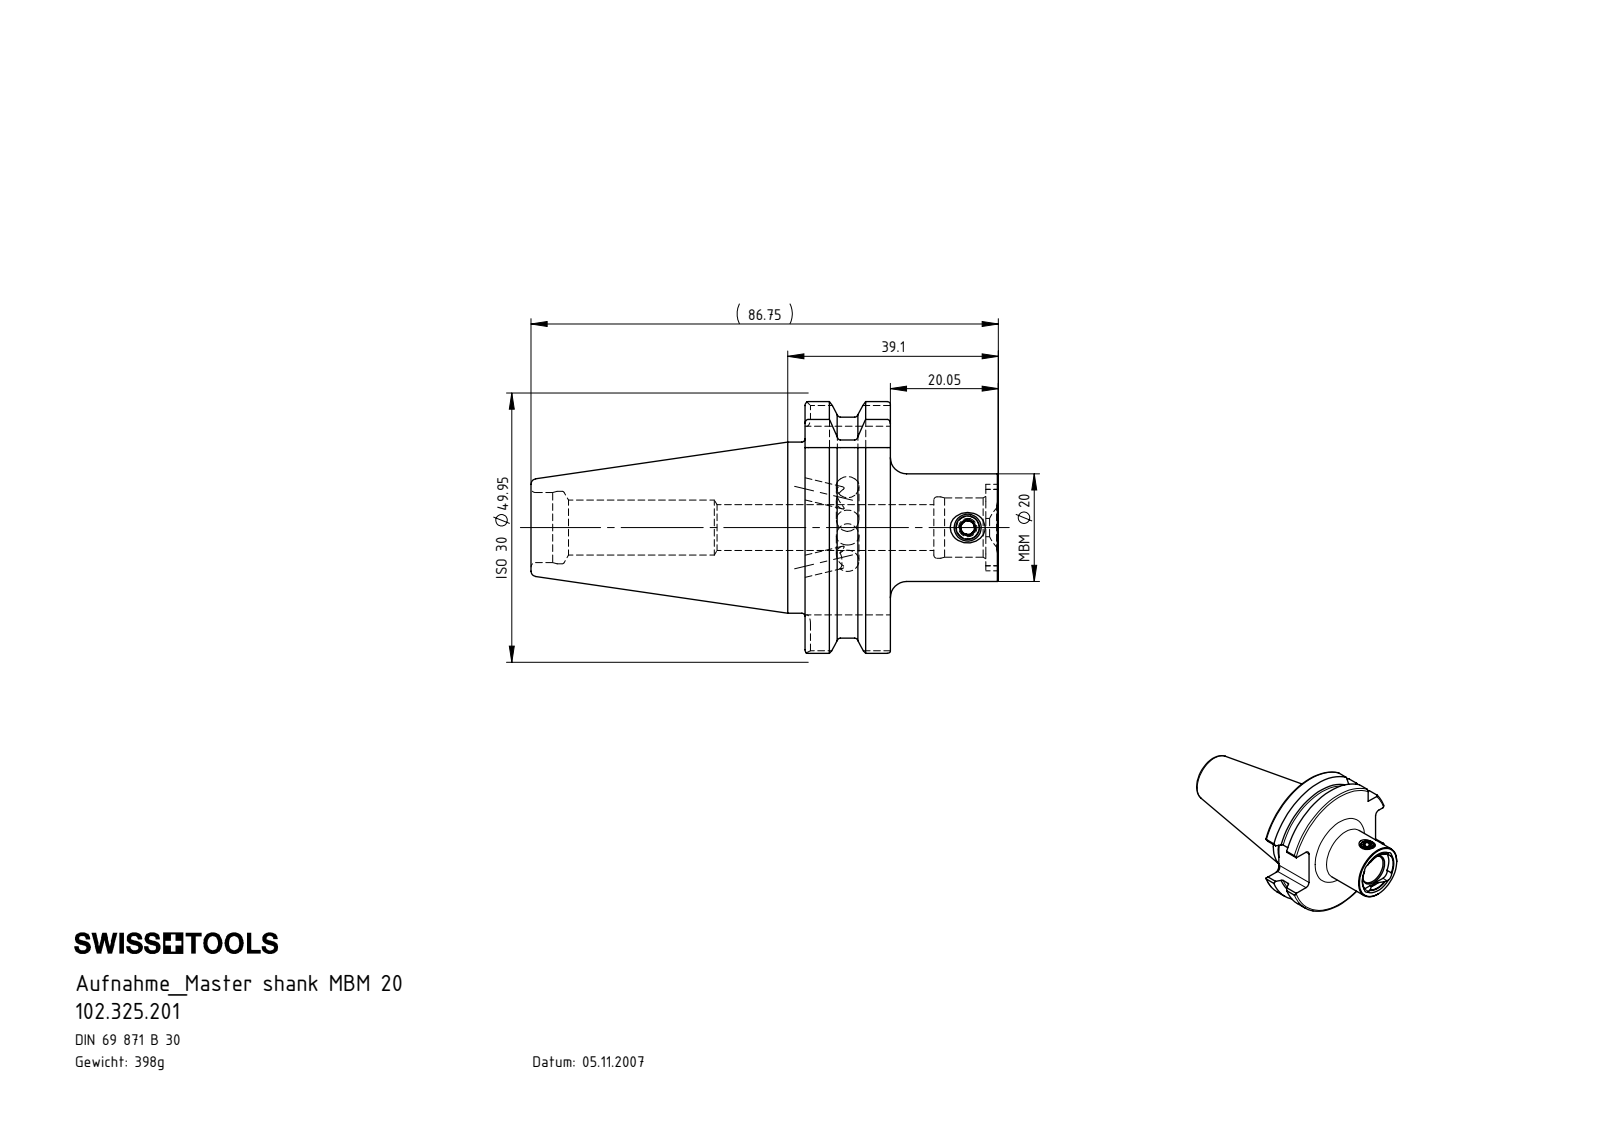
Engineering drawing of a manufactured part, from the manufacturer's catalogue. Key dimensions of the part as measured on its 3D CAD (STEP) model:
Part name (STEP PRODUCT): MB1-ER1.001.006_A; 102.325.201; SB3-MB1.K01.039_B_mit Bundkhlung
STEP written by: SolidWorks 2017 (CONFIG_CONTROL_DESIGN)
Units: millimetres
Bodies: 2 solids, 179 faces (47 planar, 59 cylindrical, 73 other)
Overall size (bounding box): 86.75 × 49.95 × 46.69
Volume: 50 714 mm³ · Surface area: 14 283 mm²
Round holes (diameter × count): ⌀4 ×2, ⌀4.2 ×2, ⌀2.5 ×1, ⌀8.5 ×1, ⌀10.2 ×1, ⌀11 ×1, ⌀11.4 ×1, ⌀13 ×1, ⌀13.45 ×1
Round bosses / shafts (diameter × count): ⌀31.75 ×1, ⌀20 ×1, ⌀5 ×1
Partial cylindrical surfaces — rounded edges, fillets, slot ends (radius × count): R1.6 ×8, R2.2 ×4, R8.03 ×1, R22.02 ×1, R24.98 ×1
Main face-to-face distances: 15.85, 35, 16.1, 35.9, 20.05, 33.55, 17.7, 2.35, 22.9, 6.8
